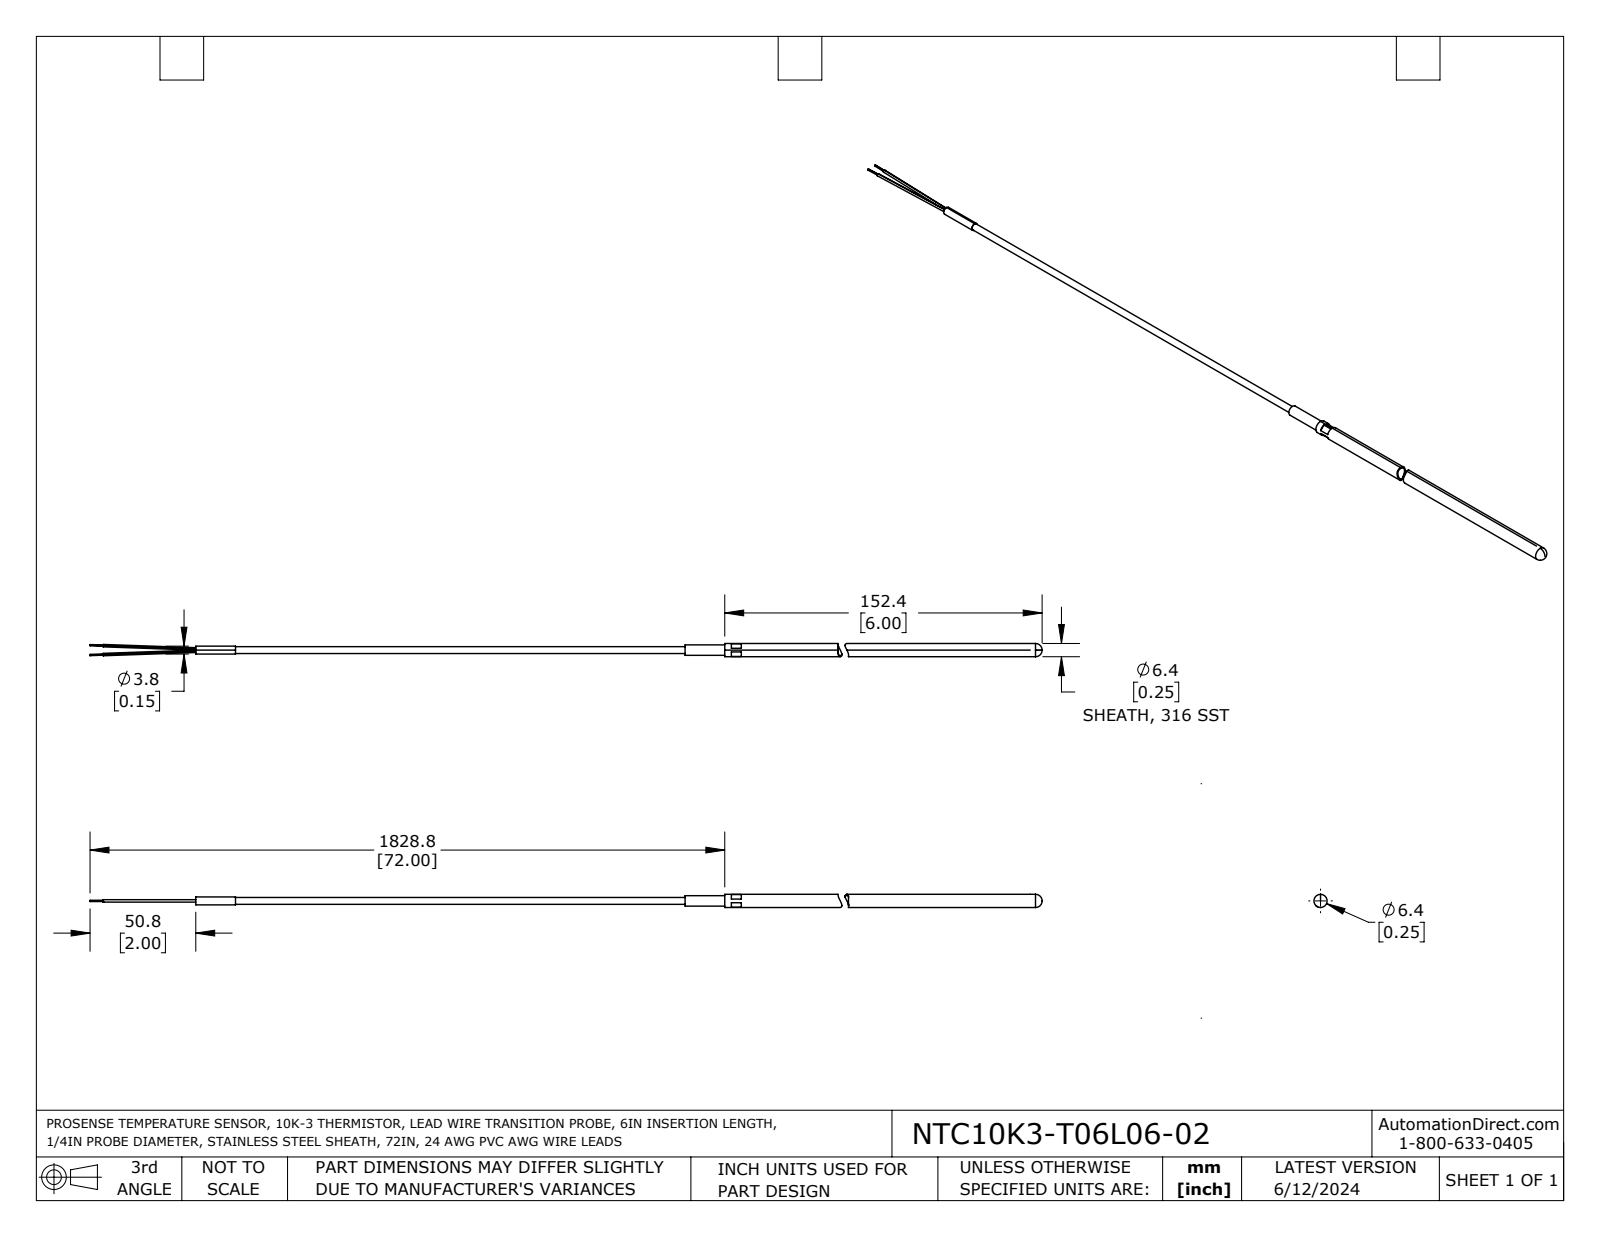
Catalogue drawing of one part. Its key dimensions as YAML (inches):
part_name: "NTC10K3-T06L06-02"
step_written_by: "SolidWorks 2021 (AUTOMOTIVE_DESIGN)"
units: inches
bodies: {solids: 3, faces: 49, planar: 25, cylindrical: 14, other: 10}
overall_size: [18, 0.25, 0.25]
volume: 0.238
surface_area: 15.73
round_holes:
  - {diameter: 0.131, count: 1}
  - {diameter: 0.187, count: 1}
  - {diameter: 0.21, count: 1}
round_bosses_or_shafts:
  - {diameter: 0.25, count: 1}
  - {diameter: 0.197, count: 1}
  - {diameter: 0.15, count: 1}
  - {diameter: 0.13, count: 1}
face_to_face_distances: [0.219, 5.775, 10.001, 15.776, 0.75, 10.126, 0.125, 5.65, 10.314, 0.313]
